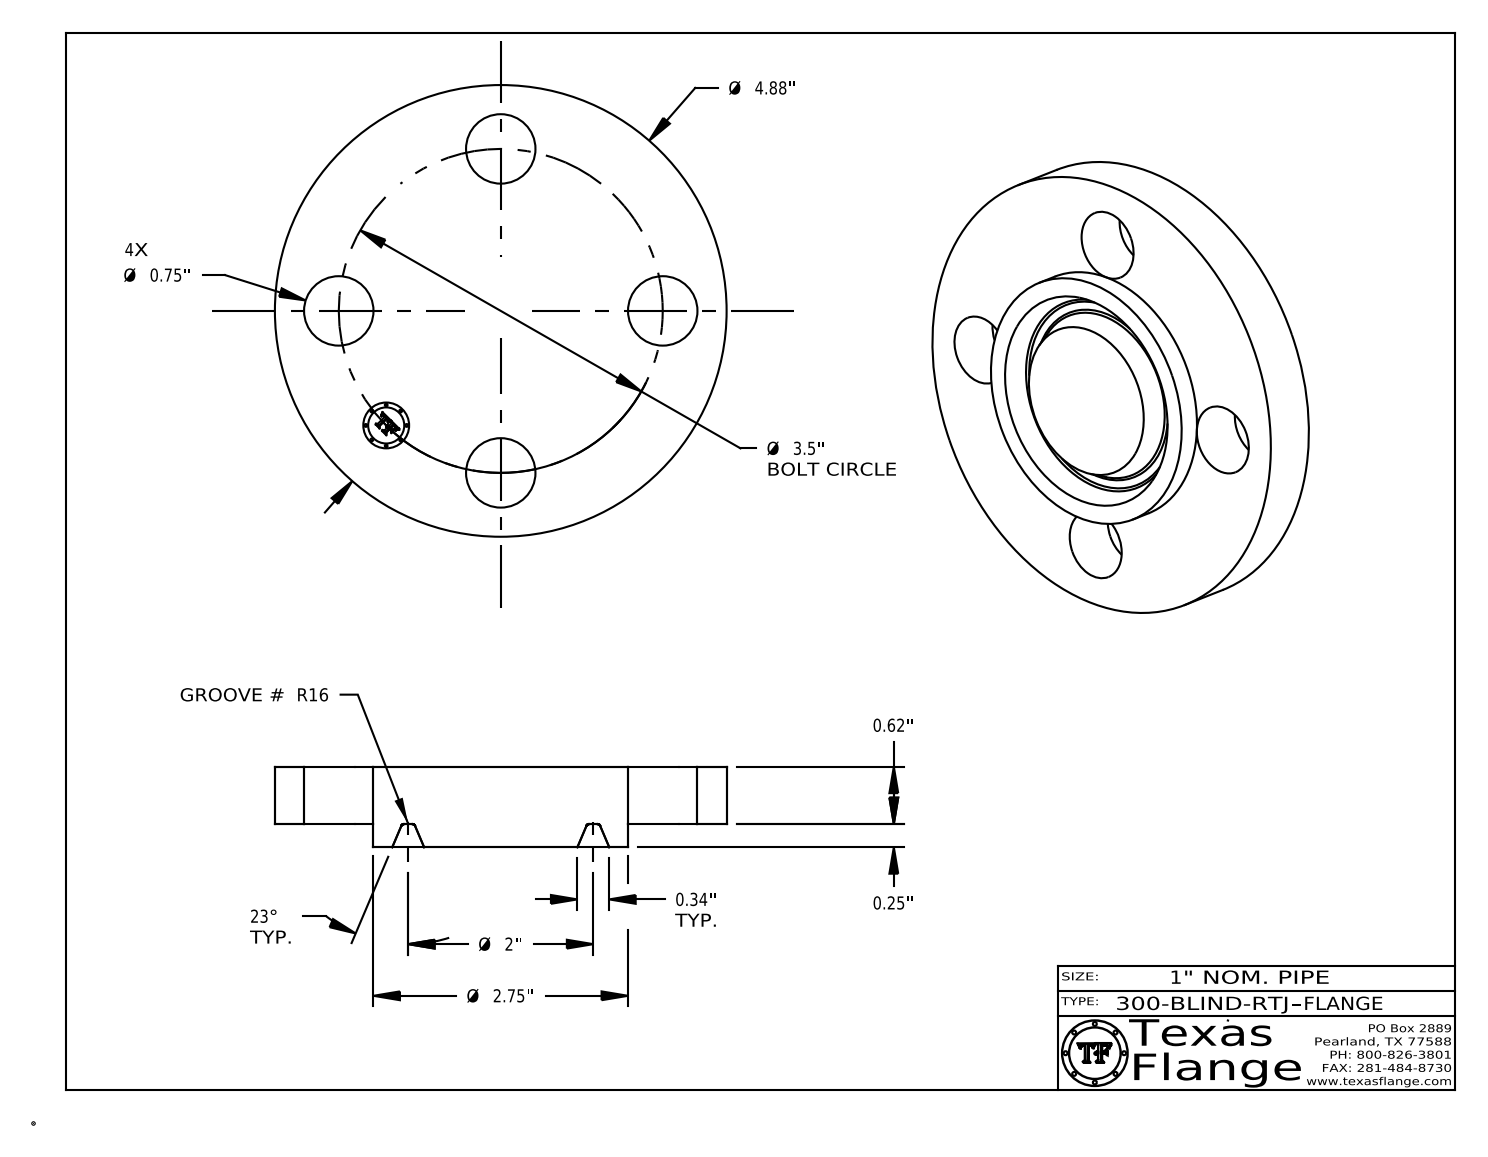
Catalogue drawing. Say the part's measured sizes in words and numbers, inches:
The part is named "300-BLIND-RTJ". Its 3-D file was written by "CATIA V5 STEP AP214 (AUTOMOTIVE_DESIGN)". It is 1 solid with 410 faces: 370 planar, 32 cylindrical and 8 other. Overall it measures 4.88 by 4.88 by 0.87 inches. Its volume is 11.61 cubic inches and its surface area 53.49 square inches. Round holes: 4 of diameter 0.75, 1 of diameter 0.495. Round bosses or shafts: 8 of diameter 0.03, 1 of diameter 4.88, 1 of diameter 2.75, 1 of diameter 0.39. The main face-to-face distances are 0.62, 0.25, 0.87, 0.015, 0.855, 0.605, 0.148, 0.145, 0.027, 0.096. The hole center spacings are 2.475, 1.339, 3.233, 3.5.
